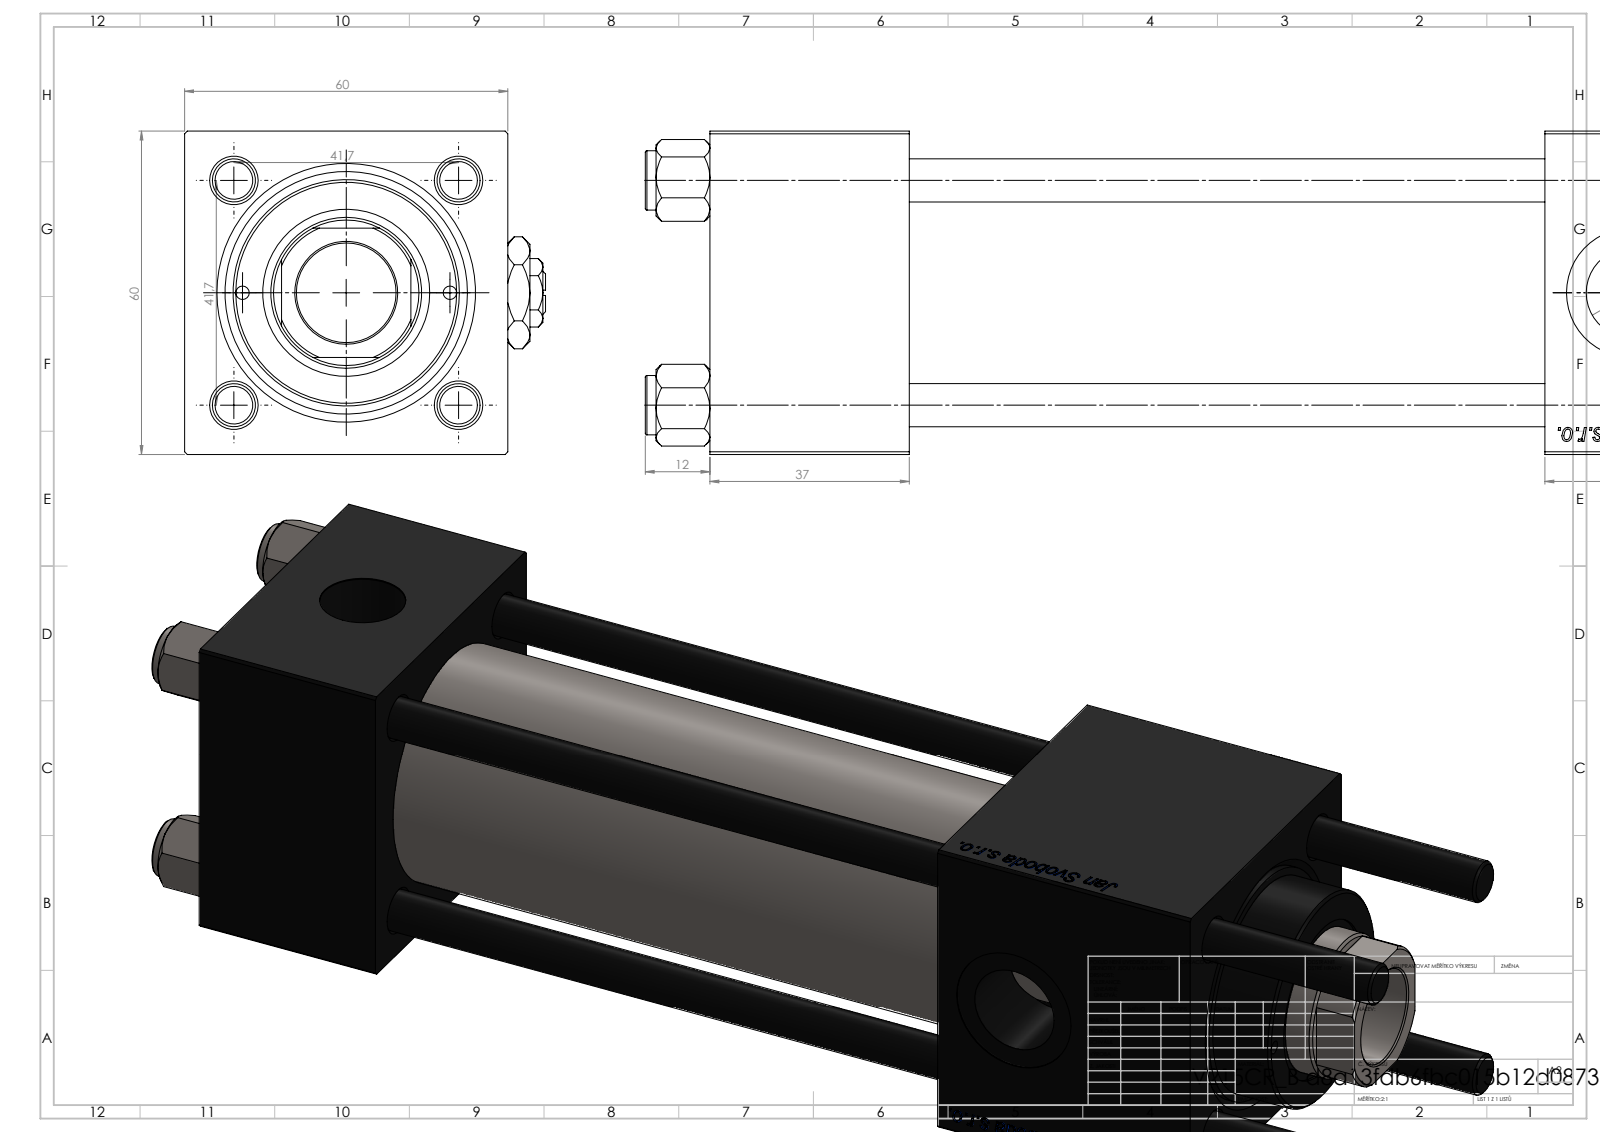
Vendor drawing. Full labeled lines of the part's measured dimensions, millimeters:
Part name (STEP PRODUCT): V215CR_B_TYCINKA; V215CR_B-1; Zatka_pro_OIL_PORT; V215CR_VCP_B (+2 more)
STEP written by: SolidWorks 2019 (CONFIG_CONTROL_DESIGN)
Units: millimetres
Bodies: 12 solids, 1207 faces (456 planar, 83 cylindrical, 668 other)
Overall size (bounding box): 255 × 67 × 60
Volume: 506 692 mm³ · Surface area: 148 758 mm²
Round holes (diameter × count): ⌀8 ×4, ⌀7 ×2, ⌀16.66 ×2, ⌀16 ×1, ⌀18.5 ×1, ⌀24 ×1, ⌀28 ×1, ⌀31 ×1, ⌀40 ×1, ⌀45 ×1
Round bosses / shafts (diameter × count): ⌀11 ×4, ⌀46 ×1, ⌀42 ×1
Partial cylindrical surfaces — rounded edges, fillets, slot ends (radius × count): R13.5 ×1
Main face-to-face distances: 60, 37, 155, 118, 53, 179.3, 142.3, 24.3, 208, 171
Hole centre spacings: 29.49, 41.7, 58.97
